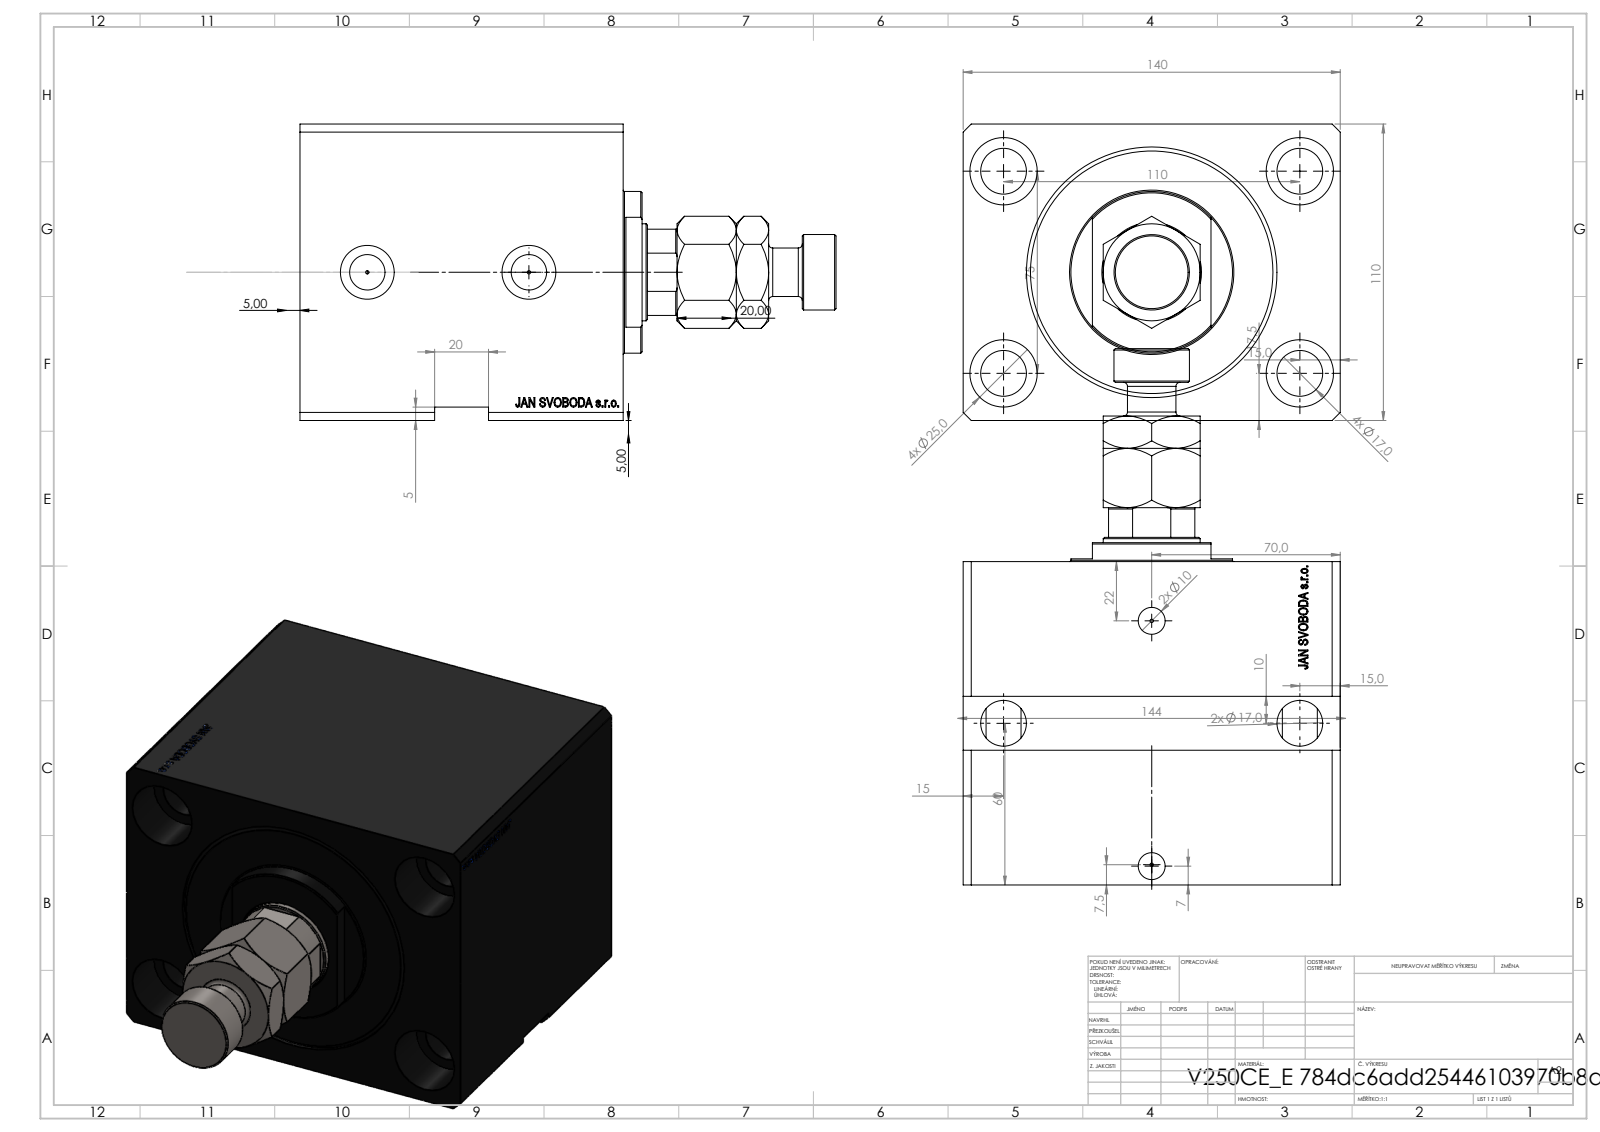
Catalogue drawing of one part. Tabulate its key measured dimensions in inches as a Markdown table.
| quantity | value |
| --- | --- |
| part name | V250CE_VC_E; V250CE_E_Body; MFA; V250CE_C_VCP |
| STEP written by | SolidWorks 2019 (CONFIG_CONTROL_DESIGN) |
| units | inches |
| bodies | 4 solids, 994 faces (488 planar, 88 cylindrical, 418 other) |
| overall size | 7.835 × 5.512 × 4.331 |
| volume | 99.22 in³ |
| surface area | 332.9 in² |
| round holes (diameter × count) | 0.669 × 6, 0.049 × 4, 0.984 × 4, 0.394 × 2, 0.518 × 2, 0.787 × 2, 1.004 × 1, 1.417 × 1, 3.15 × 1, 3.661 × 1 |
| round bosses / shafts (diameter × count) | 2.362 × 1, 1.102 × 1, 0.709 × 1 |
| partial cylindrical surfaces (radius × count) | 0.689 × 1 |
| main face-to-face distances | 4.331, 0.787, 5.512, 0.984, 4.724, 3.74, 3.937, 2.953, 1.575, 2.165 |
| hole center spacings | 2.621, 4.331, 2.632, 2.953, 2.993, 3.007, 5.242, 0.021 |
